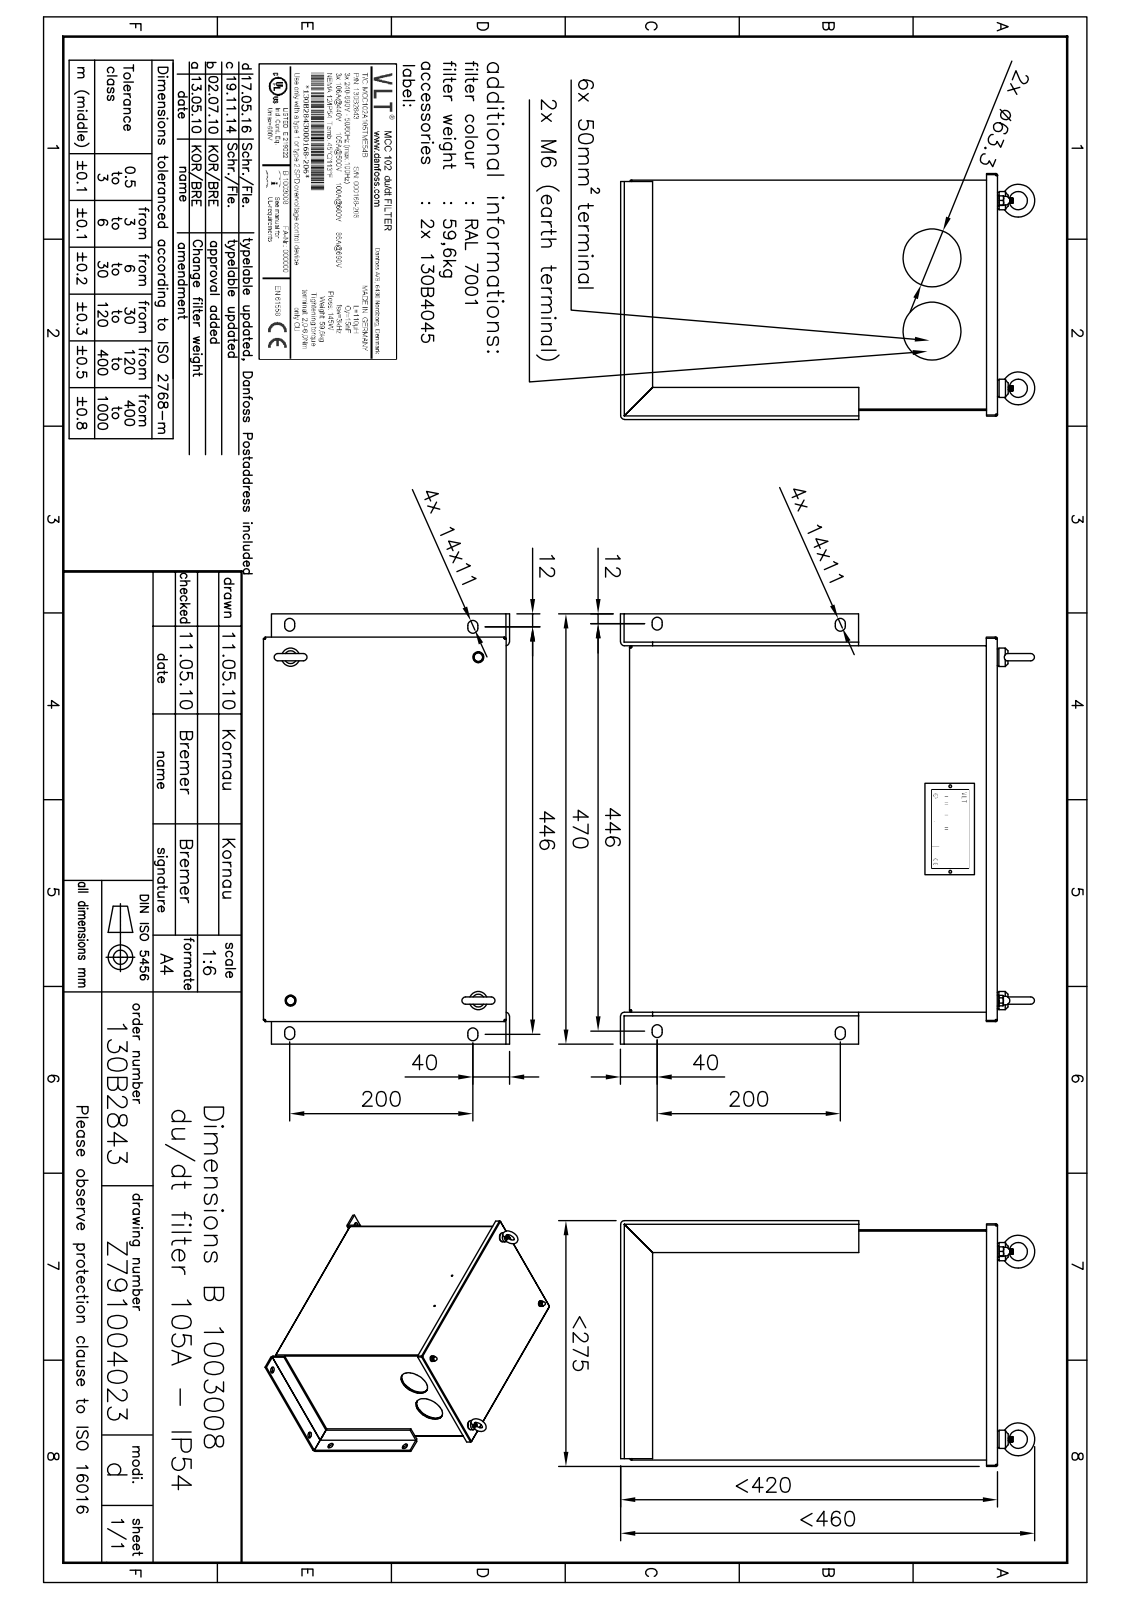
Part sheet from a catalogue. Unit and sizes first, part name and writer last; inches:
Units: inches
Overall size (bounding box): 18.504 × 17.642 × 10.575
Round holes (diameter × count): ⌀0.335 ×12, ⌀0.217 ×10, ⌀0.252 ×6, ⌀0.165 ×4, ⌀0.236 ×4, ⌀0.299 ×4, ⌀0.13 ×2, ⌀0.177 ×2, ⌀0.197 ×2, ⌀0.239 ×2, ⌀0.24 ×2, ⌀0.281 ×2
Round bosses / shafts (diameter × count): ⌀0.472 ×5, ⌀0.394 ×4, ⌀0.157 ×4, ⌀0.197 ×3, ⌀0.709 ×2, ⌀0.591 ×2, ⌀0.465 ×2, ⌀0.374 ×2
Partial cylindrical surfaces — rounded edges, fillets, slot ends (radius × count): R0.004 ×27, R0.039 ×24, R0.063 ×16, R0.217 ×16, R0.161 ×5, R0.043 ×4, R0.098 ×4, R0.276 ×4
Main face-to-face distances: 0.059, 15.689, 9.843, 15.63, 9.783, 15.748, 9.902, 6.988, 8.76, 8.701
Hole centre spacings: 0.984, 1.758, 0.879, 1.969, 2.449, 1.457, 2.953, 3.293
Volume: 1 483 in³ · Surface area: 3 895 in²
Bodies: 37 solids, 1145 faces (787 planar, 240 cylindrical, 118 other)
Part name (STEP PRODUCT): +1095-0157; curved spring lock washer_din_Spring washer DIN 128 - A6; Gehäuseschale BG 30-x IP54-105A; 130B2843 (+8 more)
STEP written by: SolidWorks 2014 (AUTOMOTIVE_DESIGN)
